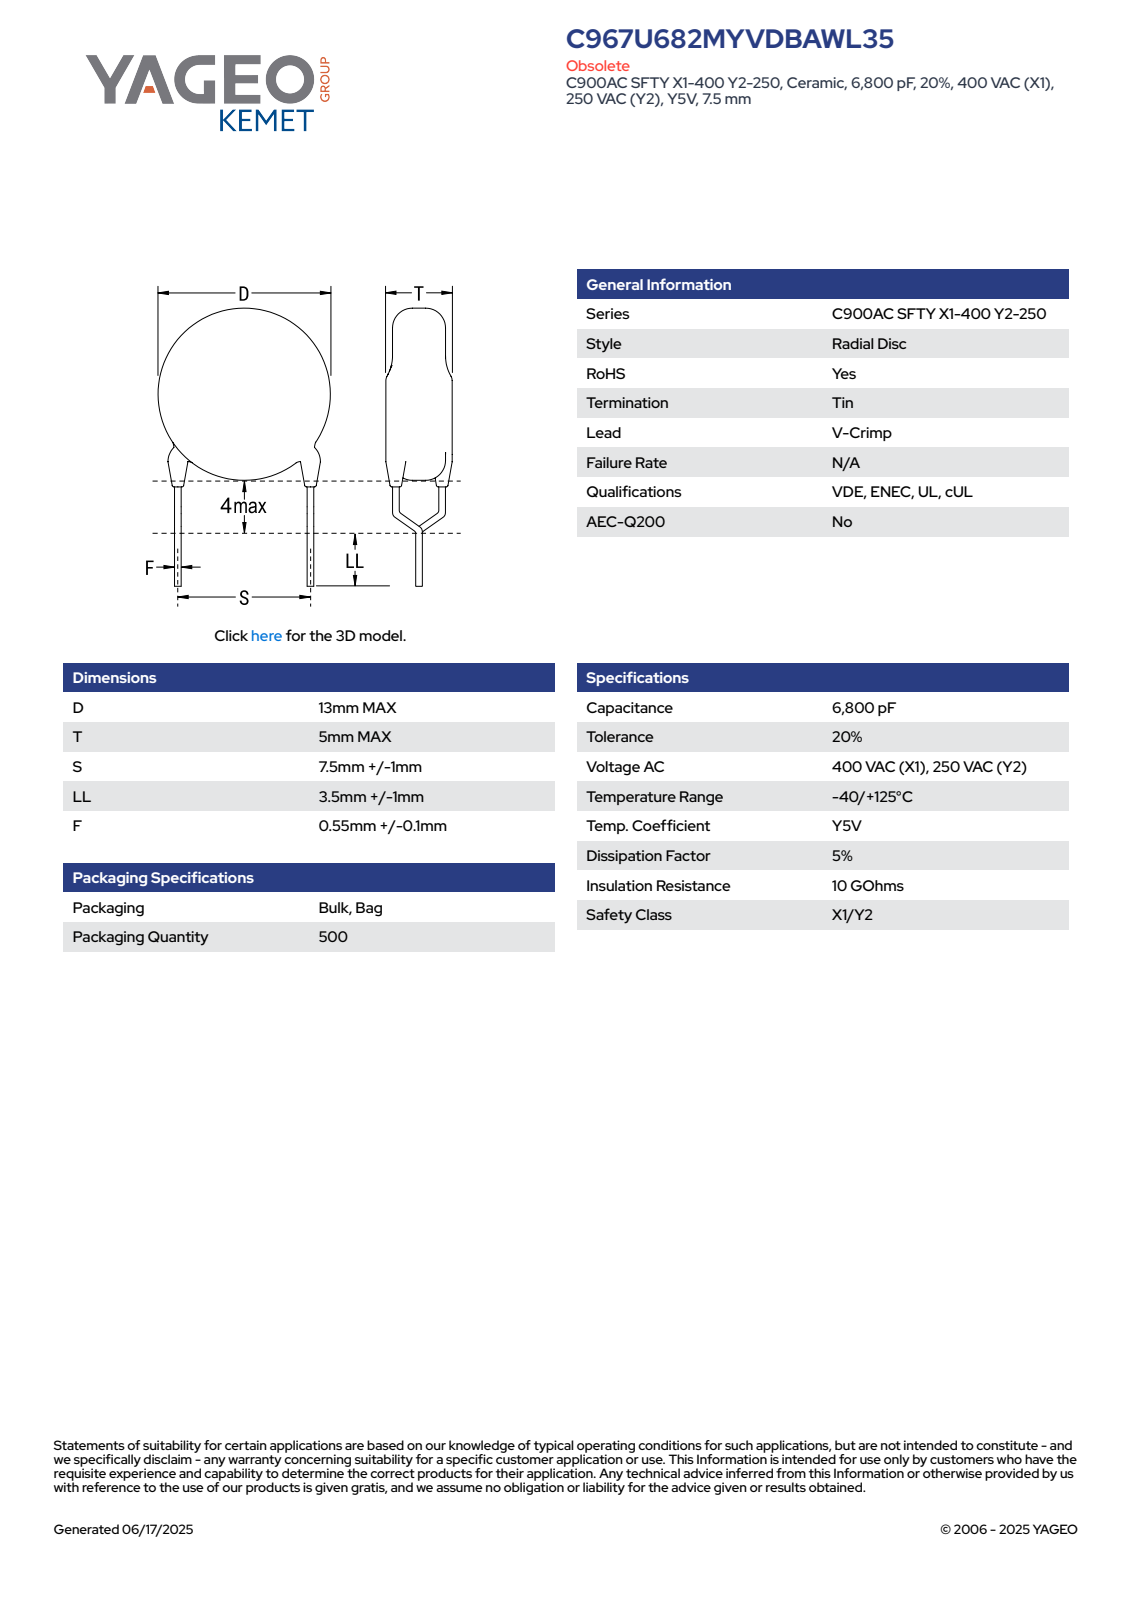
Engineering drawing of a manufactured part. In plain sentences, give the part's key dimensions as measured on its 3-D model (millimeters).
The part is named "CCD_VCC900_D13T5S7.5LL4.5F0.65". Its 3-D file was written by "SolidWorks 2014 (AUTOMOTIVE_DESIGN)". It is 5 solids with 93 faces: 65 planar, 16 cylindrical and 12 other. Overall it measures 21.3 by 13 by 5 millimeters. Its volume is 654 cubic millimeters and its surface area 493 square millimeters. Round bosses or shafts: 6 of diameter 0.65, 1 of diameter 13. The main face-to-face distances are 5, 7.4, 15.64, 8.24, 13.95, 6.55, 1.69, 0.46, 6.9, 0.63.
